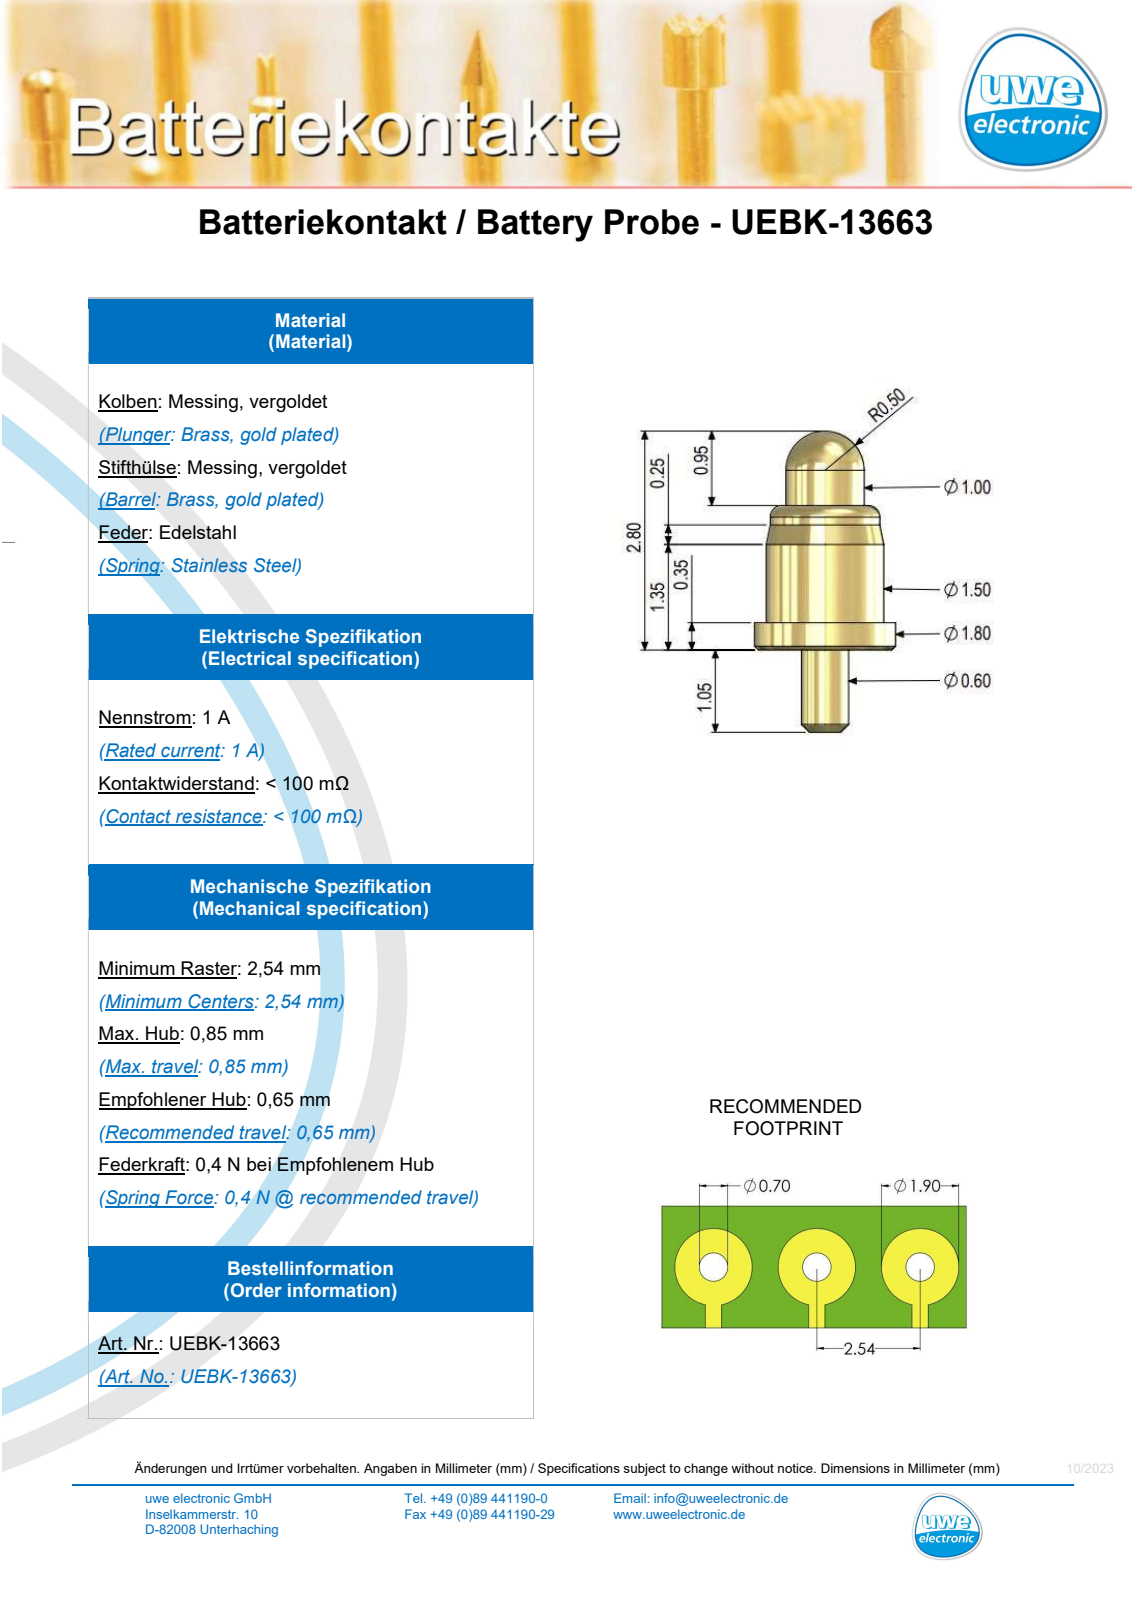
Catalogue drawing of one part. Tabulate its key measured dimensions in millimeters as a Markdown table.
| quantity | value |
| --- | --- |
| part name | UEBK-13663_step |
| STEP written by | SolidWorks 2022 (AUTOMOTIVE_DESIGN) |
| units | millimeters |
| bodies | 1 solid, 24 faces (4 planar, 10 cylindrical, 10 other) |
| overall size | 3.85 × 1.8 × 1.8 |
| volume | 4 mm³ |
| surface area | 17 mm² |
| round bosses / shafts (diameter × count) | 1.8 × 1, 1.5 × 1, 1.4 × 1, 1 × 1, 0.6 × 1 |
| main face-to-face distances | 0.35, 1.5, 1.85, 2.9, 1.4, 1.05 |
